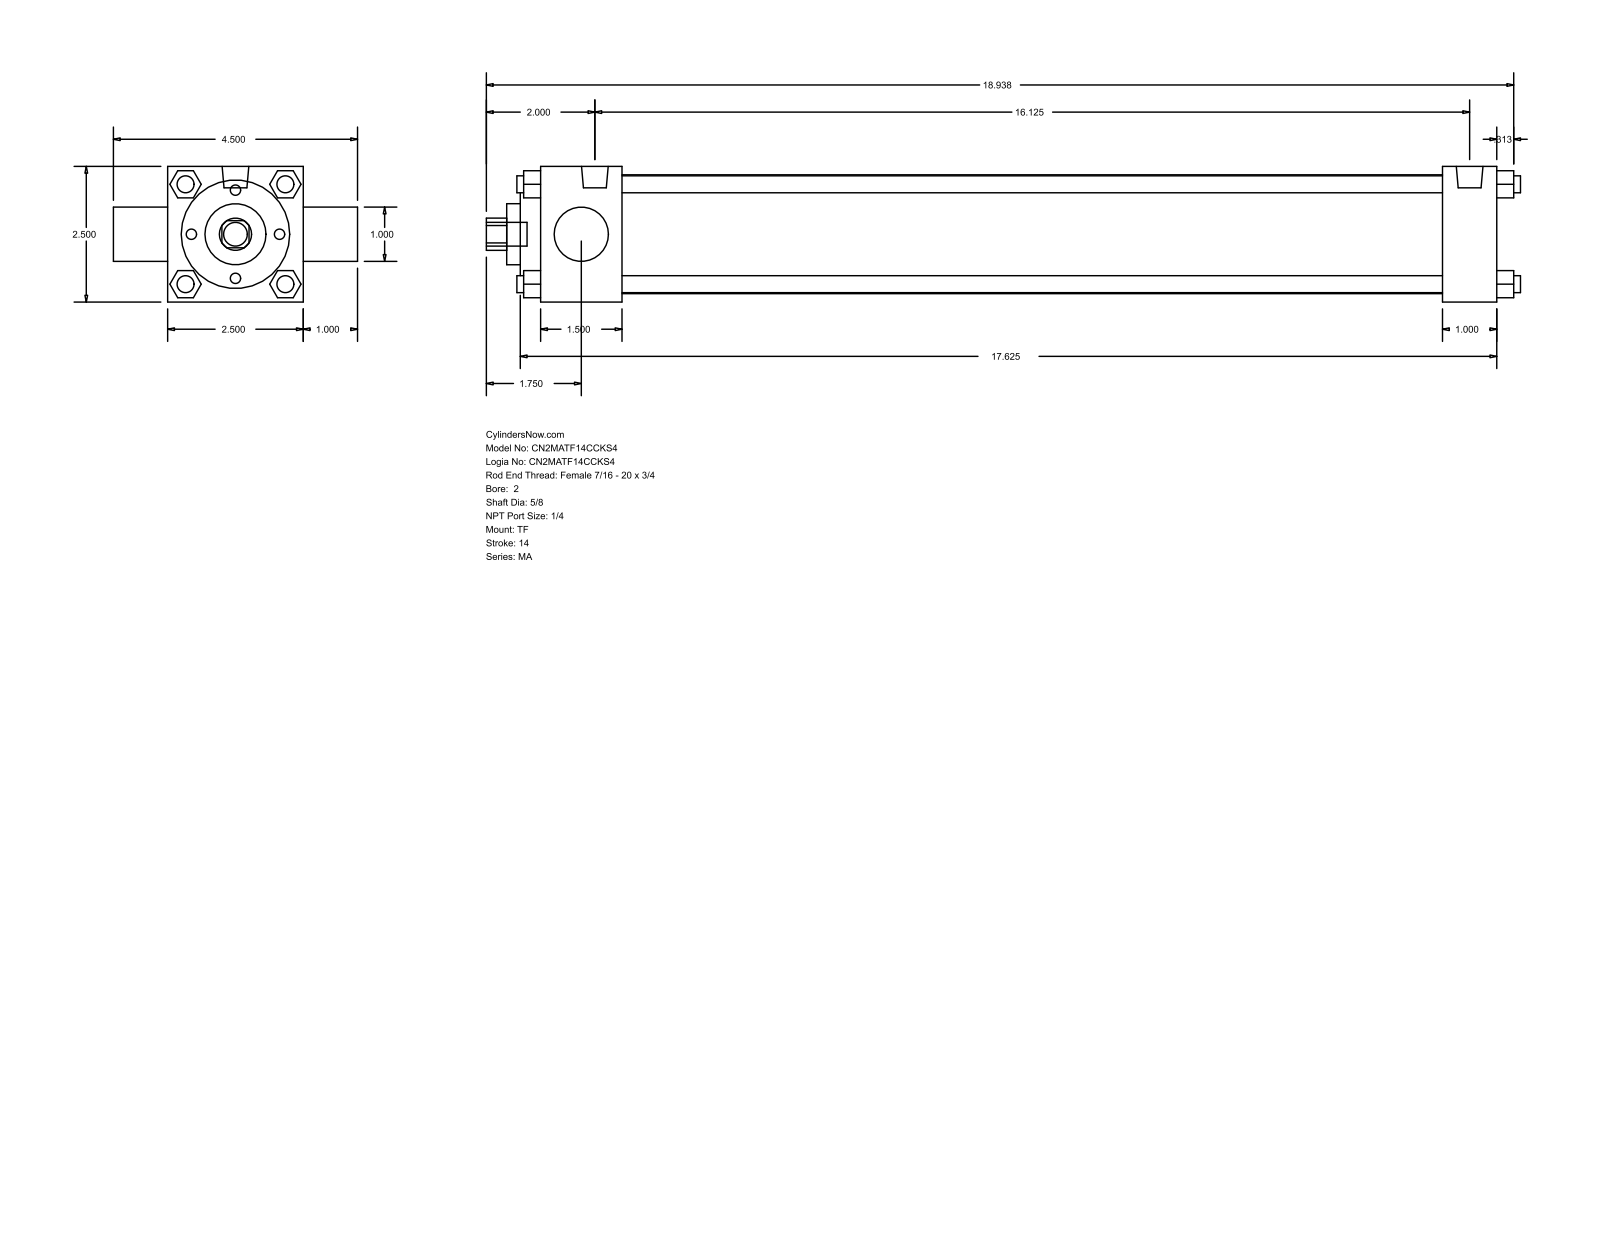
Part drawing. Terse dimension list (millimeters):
name: MA_TF__0200_0.625
written by: GSSL Pune (CONFIG_CONTROL_DESIGN)
unit: mm
bodies: 0 solids, 122 faces (93 planar, 29 cylindrical, 0 other)
size: 484.19 × 114.3 × 63.5
holes: 1× ⌀15.88, 1× ⌀25.4, 1× ⌀28.57, 1× ⌀50.8, 1× ⌀55.63
bosses: 7× ⌀7.94, 2× ⌀12.49, 1× ⌀11.11
rounds: 1× R7.54
face distances: 63.5, 38.1, 12.7, 9.52, 447.67, 422.28, 384.18, 409.57, 25.39, 47.62
